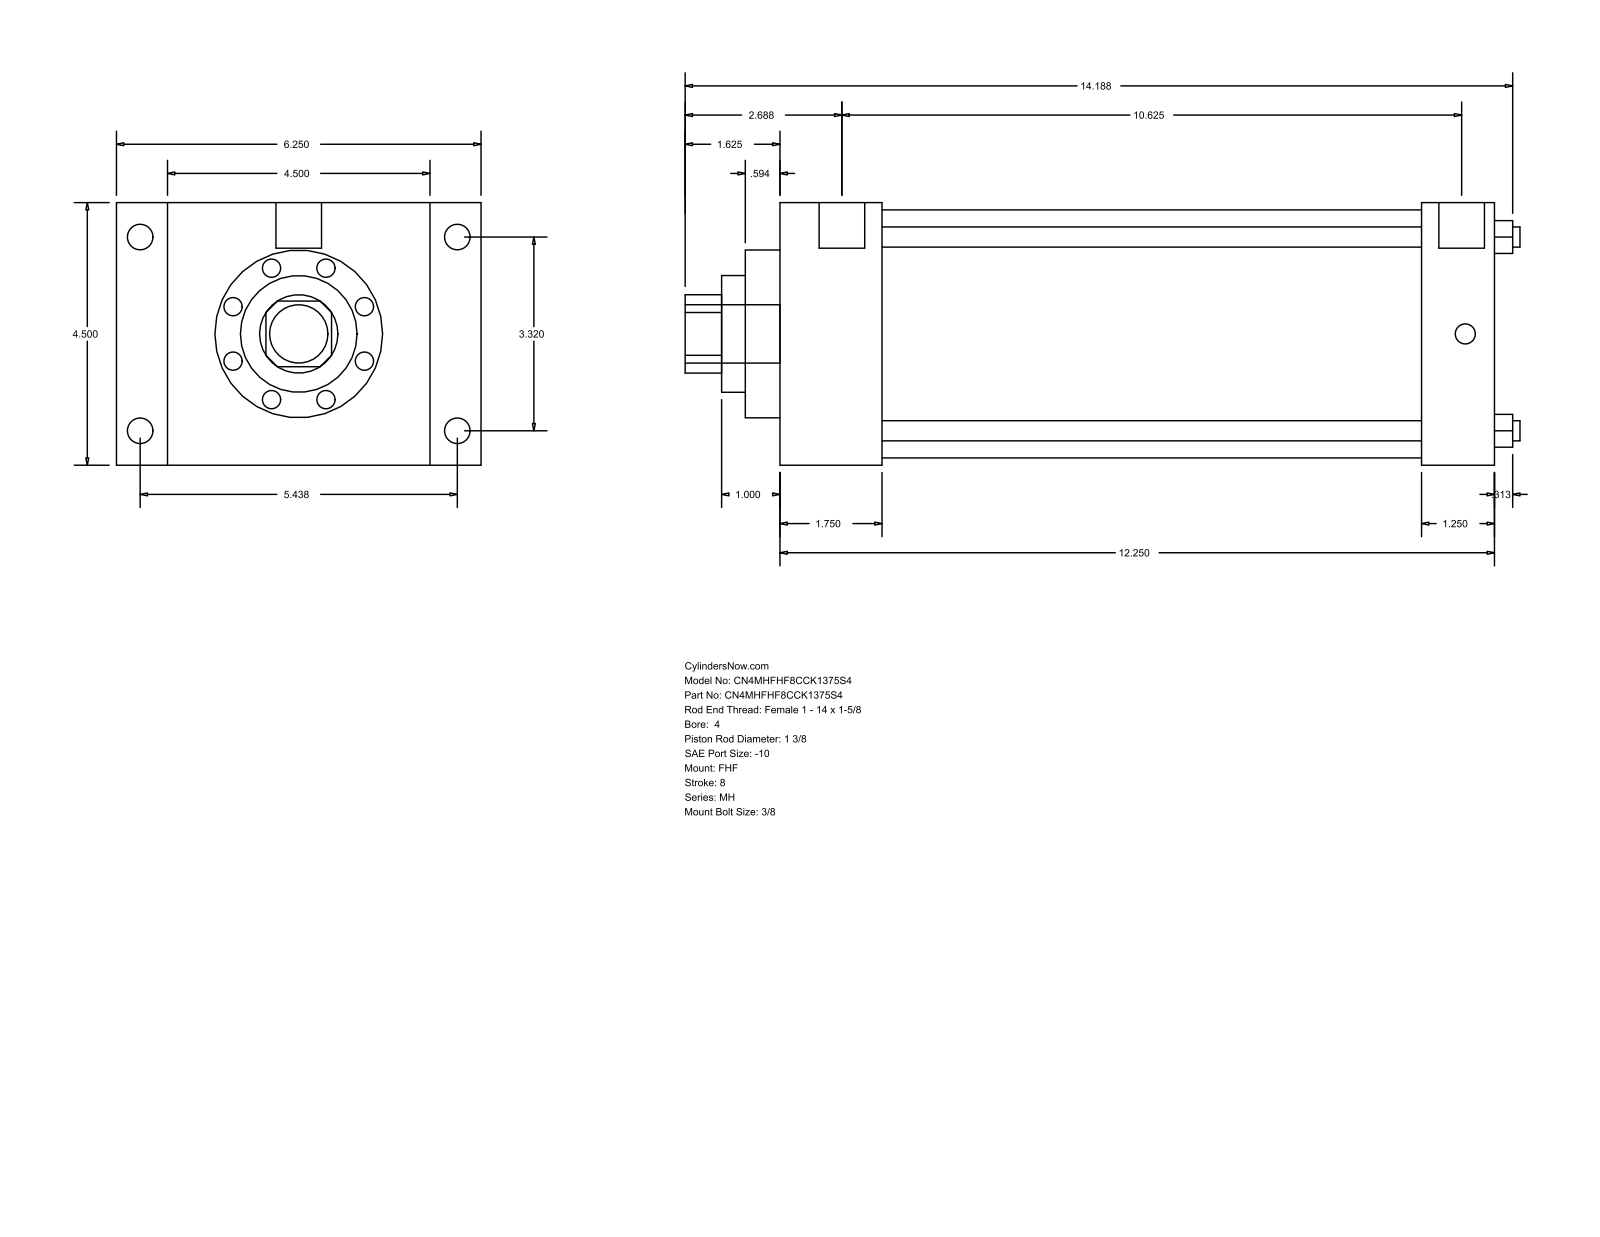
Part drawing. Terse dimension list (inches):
name: MH_FHF__0400_1.375
written by: GSSL Pune (CONFIG_CONTROL_DESIGN)
unit: in
bodies: 0 solids, 90 faces (61 planar, 29 cylindrical, 0 other)
size: 14.313 × 6.25 × 4.5
holes: 4× ⌀0.345, 1× ⌀1.375, 1× ⌀2, 1× ⌀2.875, 1× ⌀4.25
bosses: 4× ⌀0.438, 4× ⌀0.344, 2× ⌀0.781, 1× ⌀1
rounds: 1× R0.672
face distances: 4.5, 12.25, 1.75, 10.5, 0.875, 5.375, 6.25, 11, 9.25, 1.25
hole spacings: 2.347, 3.32, 4.695
